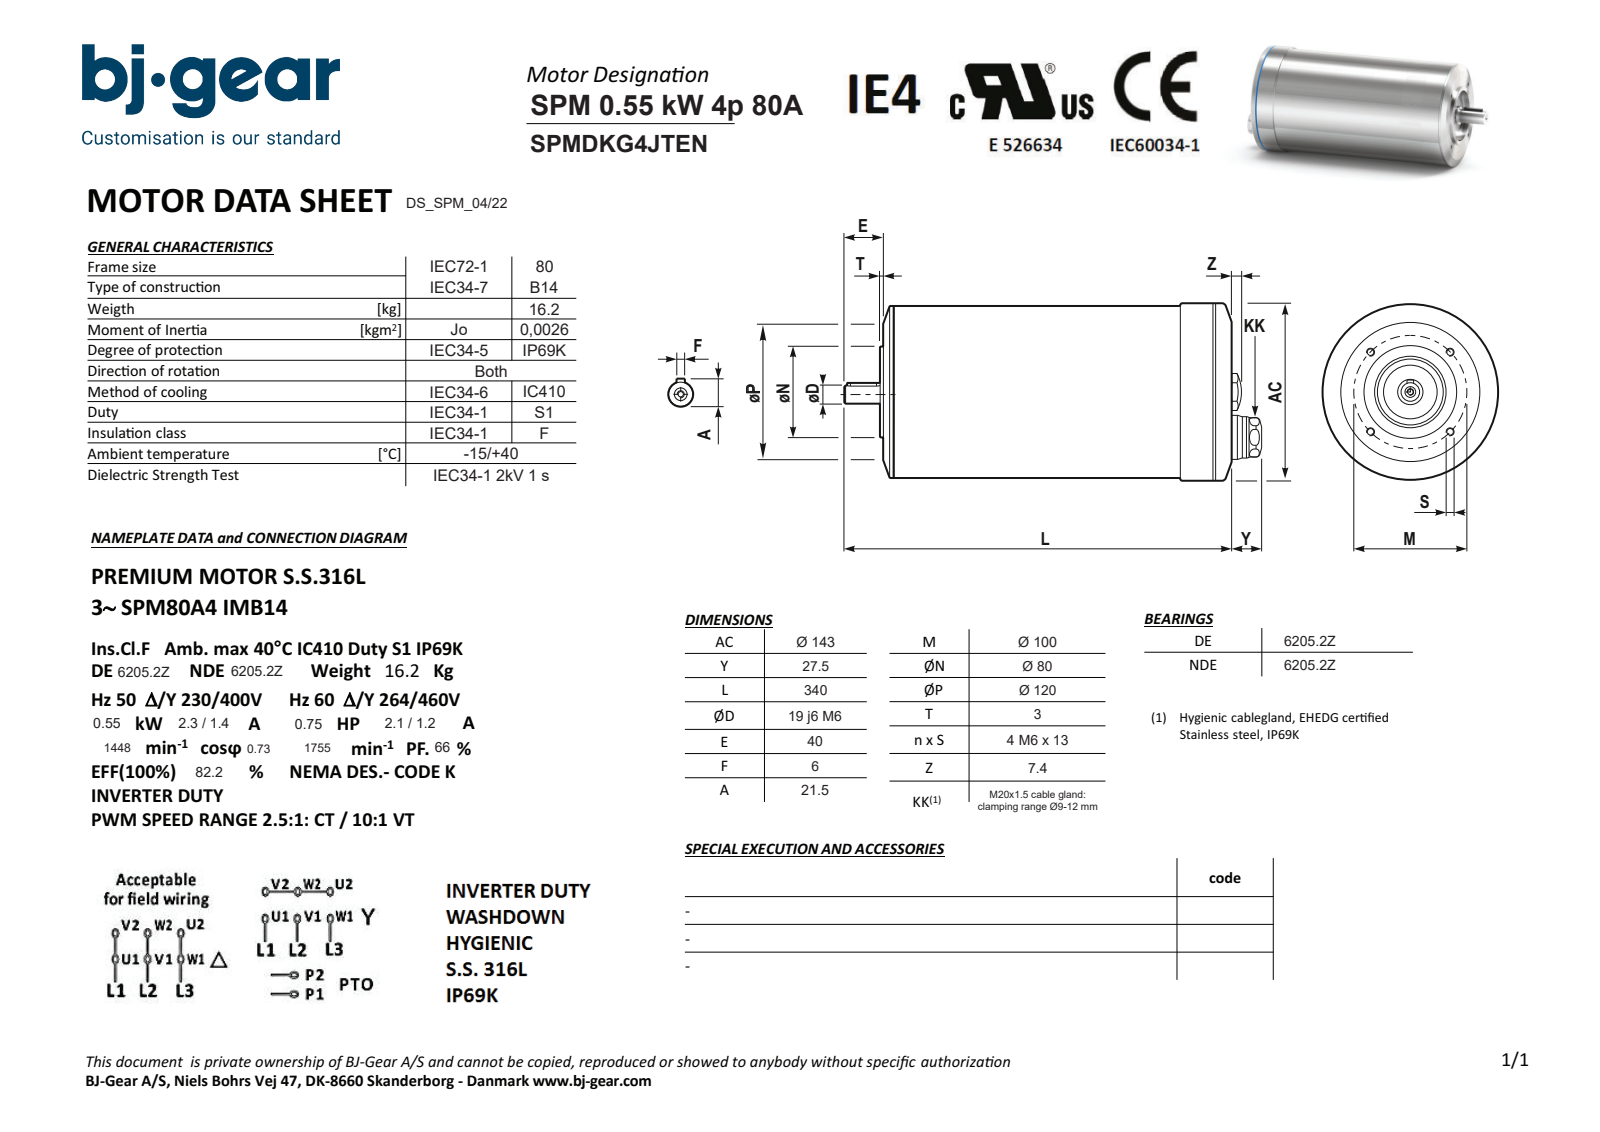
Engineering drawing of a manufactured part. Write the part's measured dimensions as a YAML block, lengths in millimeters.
part_name: "SPMDKG4JTENN4KSA1-N---NNN"
step_written_by: "Solid Edge (AUTOMOTIVE_DESIGN)"
units: millimeters
bodies: {solids: 1, faces: 87, planar: 30, cylindrical: 32, other: 25}
overall_size: [367.5, 143, 143]
volume: 4570000
surface_area: 168444
round_holes:
  - {diameter: 4.92, count: 5}
  - {diameter: 6.4, count: 1}
  - {diameter: 7, count: 1}
  - {diameter: 13.4, count: 1}
  - {diameter: 68, count: 1}
round_bosses_or_shafts:
  - {diameter: 143, count: 1}
  - {diameter: 142.98, count: 1}
  - {diameter: 139, count: 1}
  - {diameter: 138.98, count: 1}
  - {diameter: 80, count: 1}
  - {diameter: 25, count: 1}
  - {diameter: 20, count: 1}
  - {diameter: 19, count: 1}
partial_cylinders:
  - {radius: 3, count: 2}
  - {radius: 12.8, count: 1}
face_to_face_distances: [300, 6, 294, 9, 303, 3, 24, 340, 46, 40]
hole_center_spacings: [50.01, 70.72, 35.46, 81.44, 100.01, 38]
